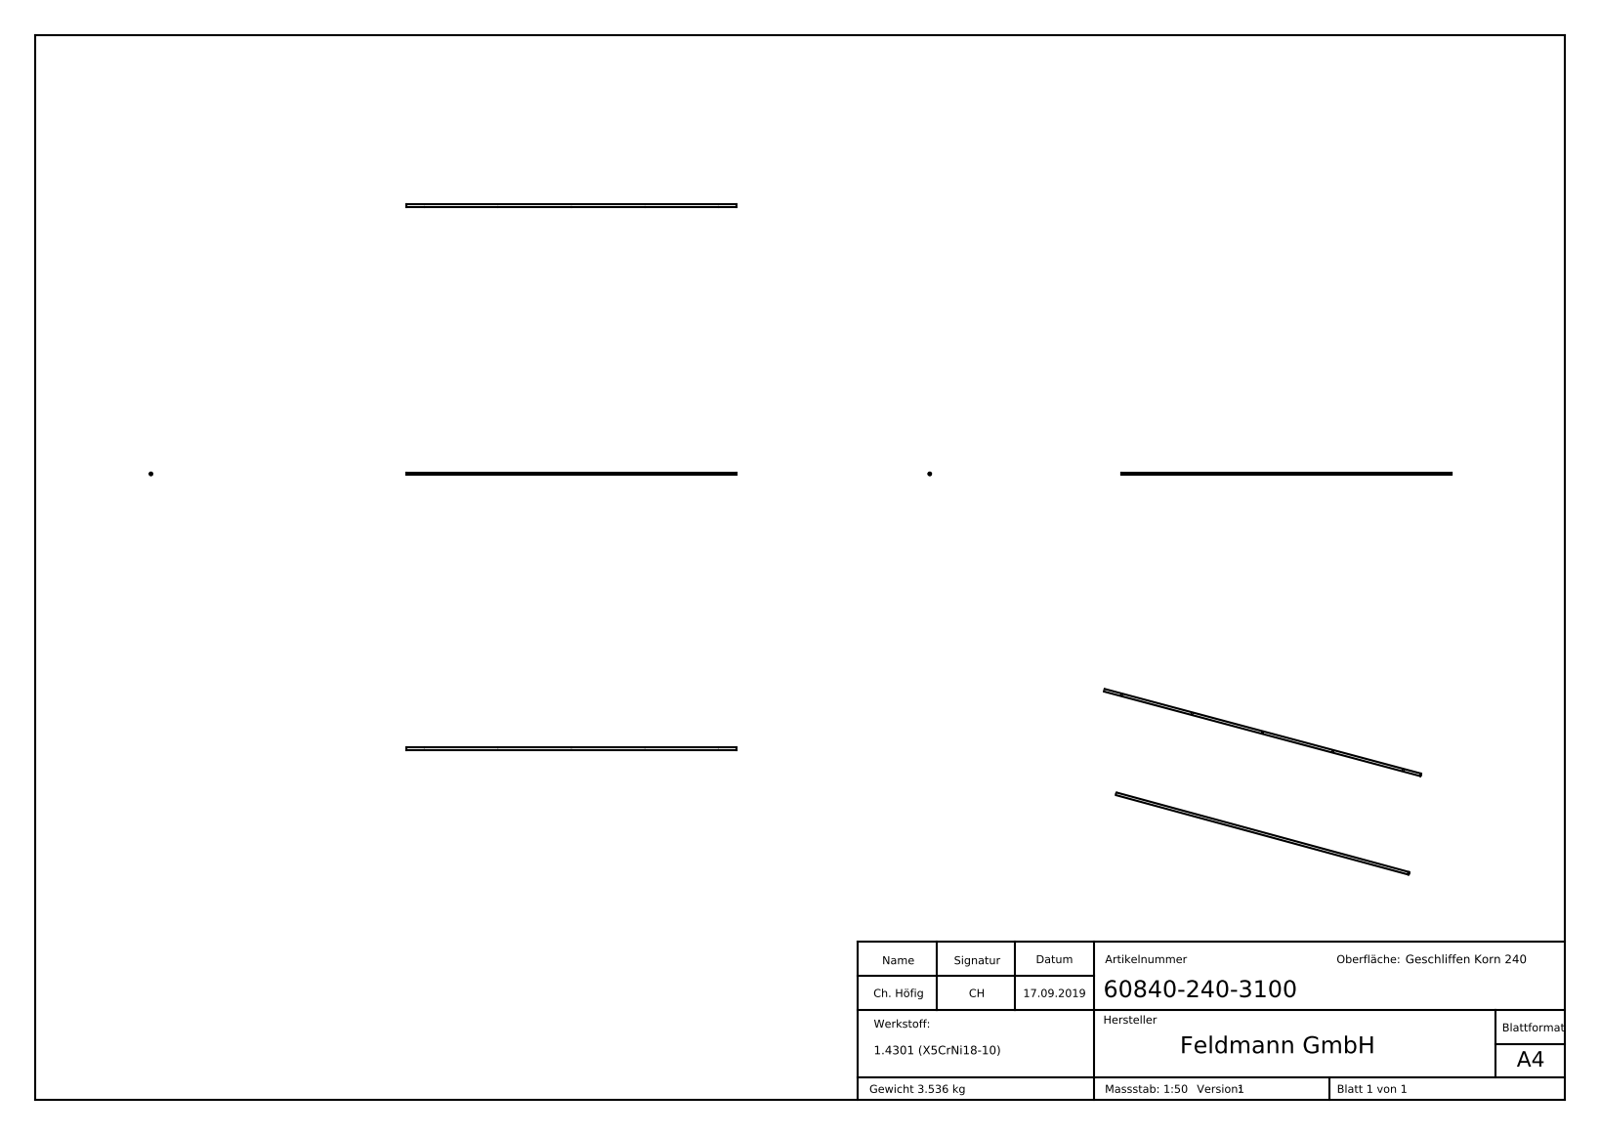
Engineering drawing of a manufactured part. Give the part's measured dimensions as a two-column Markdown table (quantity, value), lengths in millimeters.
| quantity | value |
| --- | --- |
| part name | 60840-240-3100 |
| STEP written by | SolidWorks 2015 (CONFIG_CONTROL_DESIGN) |
| units | millimeters |
| bodies | 1 solid, 305 faces (108 planar, 58 cylindrical, 139 other) |
| overall size | 3100 × 25 × 25 |
| volume | 447 623 mm³ |
| surface area | 448 144 mm² |
| round holes (diameter × count) | 6.8 × 5, 21 × 1 |
| round bosses / shafts (diameter × count) | 25 × 1 |
| partial cylindrical surfaces (radius × count) | 10.6 × 1 |
| main face-to-face distances | 3100, 2.97, 0.39, 3.66, 3.27, 8.4, 7.11, 3.44, 3.67, 3.09 |
| hole center spacings | 690, 1380, 2070, 2760 |
